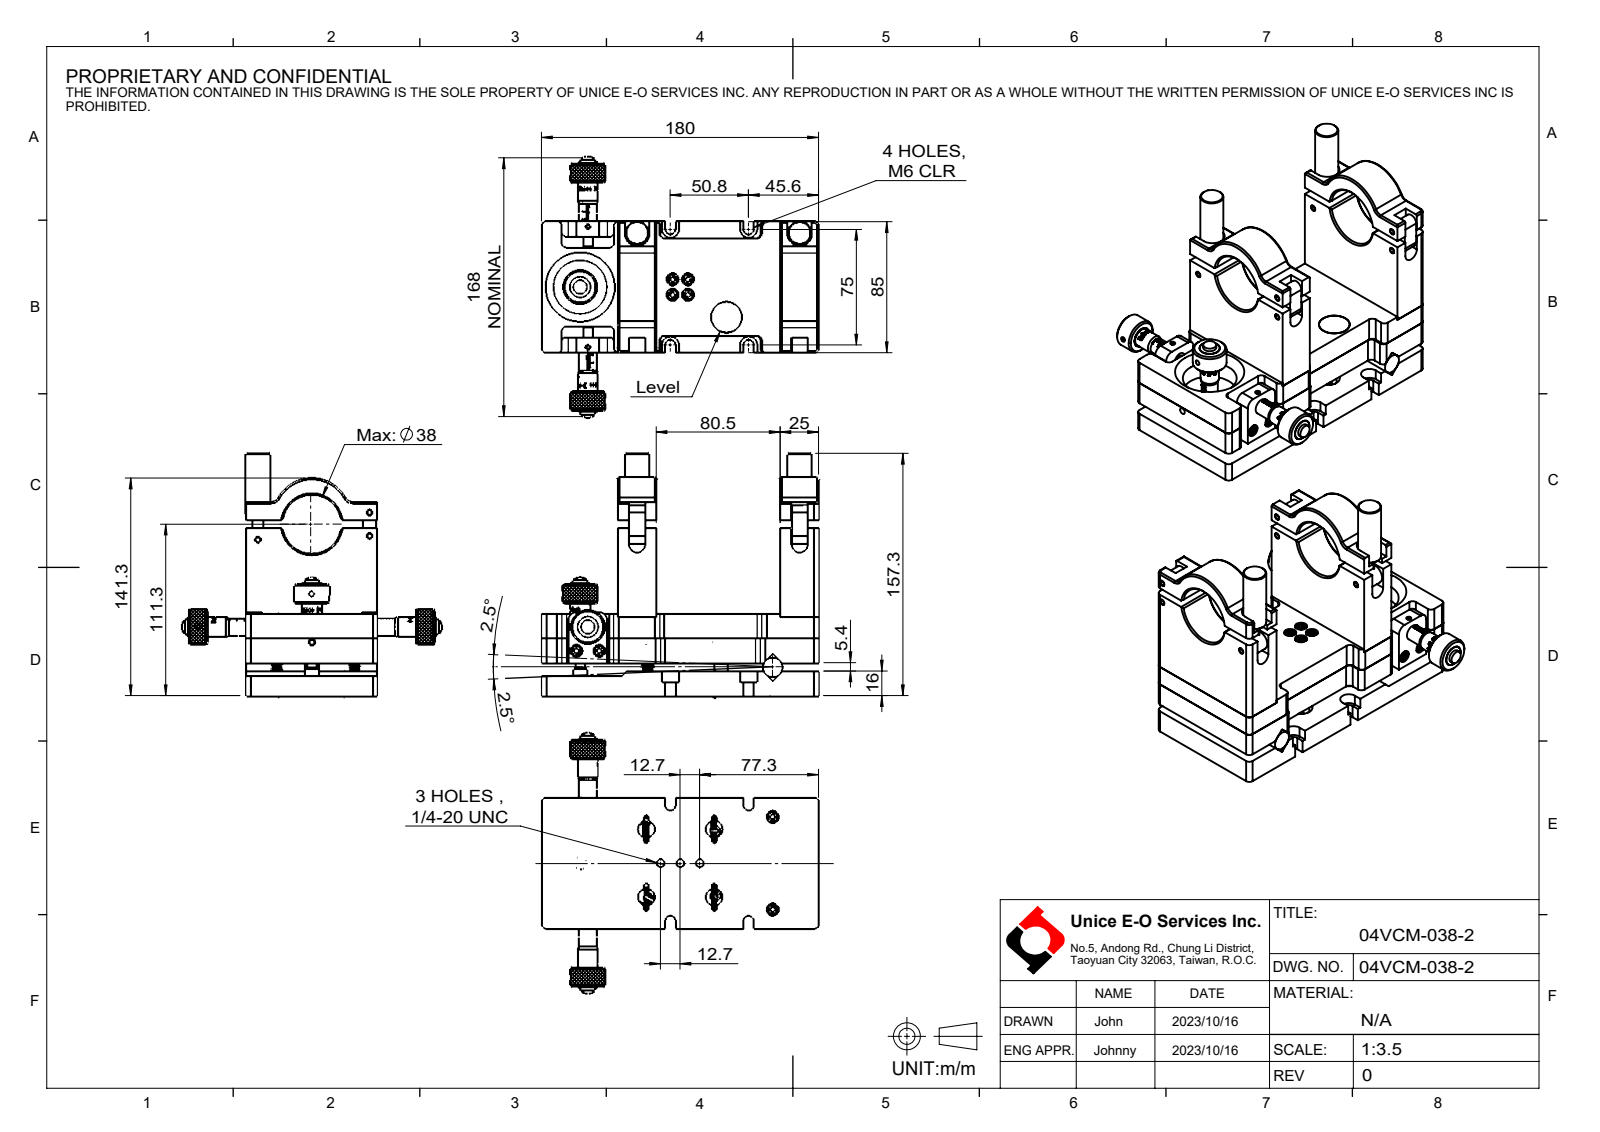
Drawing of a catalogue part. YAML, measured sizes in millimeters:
part_name: "04VCM-038-2"
step_written_by: "SolidWorks 2022 (CONFIG_CONTROL_DESIGN)"
units: millimeters
bodies: {solids: 0, faces: 623, planar: 333, cylindrical: 206, other: 84}
overall_size: [180, 168, 157.78]
round_holes:
  - {diameter: 8, count: 8}
  - {diameter: 3.3, count: 5}
  - {diameter: 1.2, count: 4}
  - {diameter: 11, count: 4}
  - {diameter: 4, count: 3}
  - {diameter: 5.11, count: 3}
  - {diameter: 13.3, count: 2}
  - {diameter: 4.3, count: 1}
  - {diameter: 8.9, count: 1}
  - {diameter: 20, count: 1}
  - {diameter: 35, count: 1}
  - {diameter: 38.2, count: 1}
round_bosses_or_shafts:
  - {diameter: 1.6, count: 4}
  - {diameter: 13, count: 3}
  - {diameter: 22, count: 2}
  - {diameter: 15, count: 2}
  - {diameter: 12, count: 2}
  - {diameter: 10.5, count: 2}
  - {diameter: 8.5, count: 2}
  - {diameter: 6, count: 2}
partial_cylinders:
  - {radius: 3, count: 32}
  - {radius: 1.5, count: 8}
  - {radius: 1, count: 6}
  - {radius: 5, count: 6}
  - {radius: 3.4, count: 4}
  - {radius: 5.6, count: 4}
  - {radius: 0.5, count: 2}
  - {radius: 4.5, count: 2}
face_to_face_distances: [16, 21.4, 37.5, 16.1, 37.4, 105.5, 25, 5.4, 21.5, 85]
hole_center_spacings: [31.91, 44, 7.07, 9.18, 10, 18.39, 23.88, 24.04]
